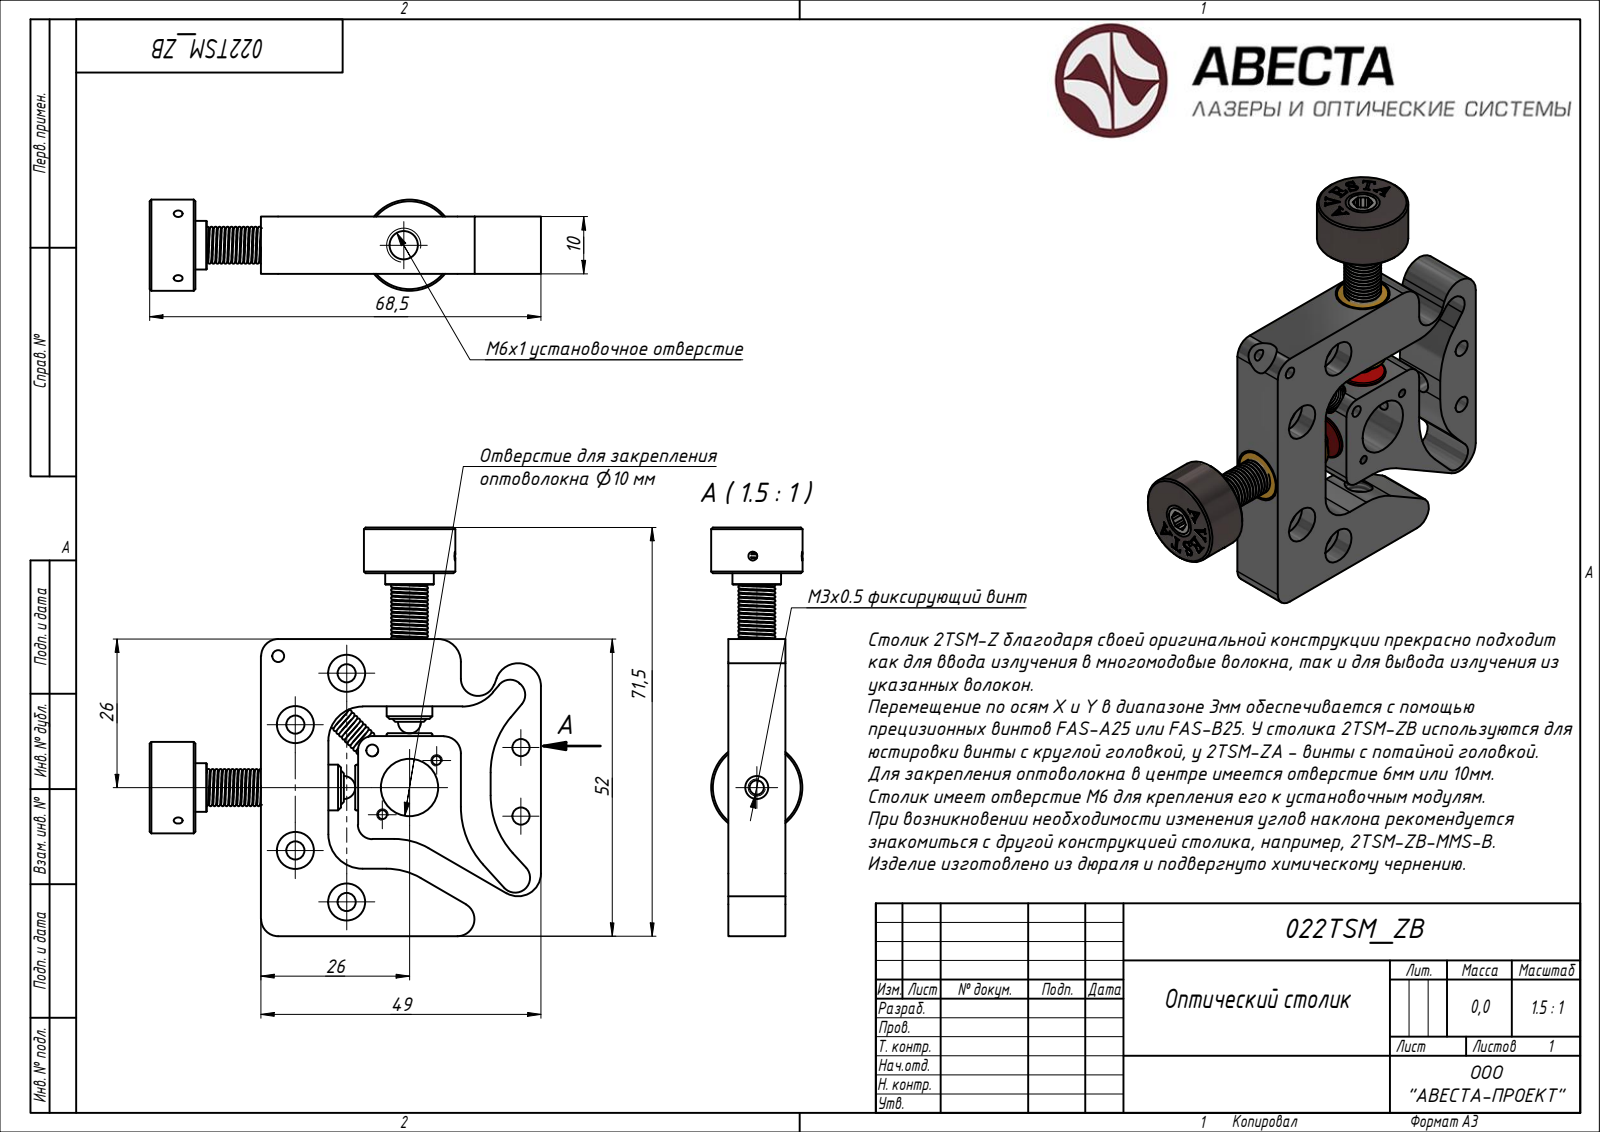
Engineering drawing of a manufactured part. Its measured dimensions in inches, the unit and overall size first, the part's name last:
Units: inches
Overall size (bounding box): 2.815 × 2.697 × 0.63
Bodies: 9 solids, 627 faces (0 planar, 0 cylindrical, 627 other)
Part name (STEP PRODUCT): Block 01; Block 02
STEP written by: ST-DEVELOPER v15 (AUTOMOTIVE_DESIGN)
